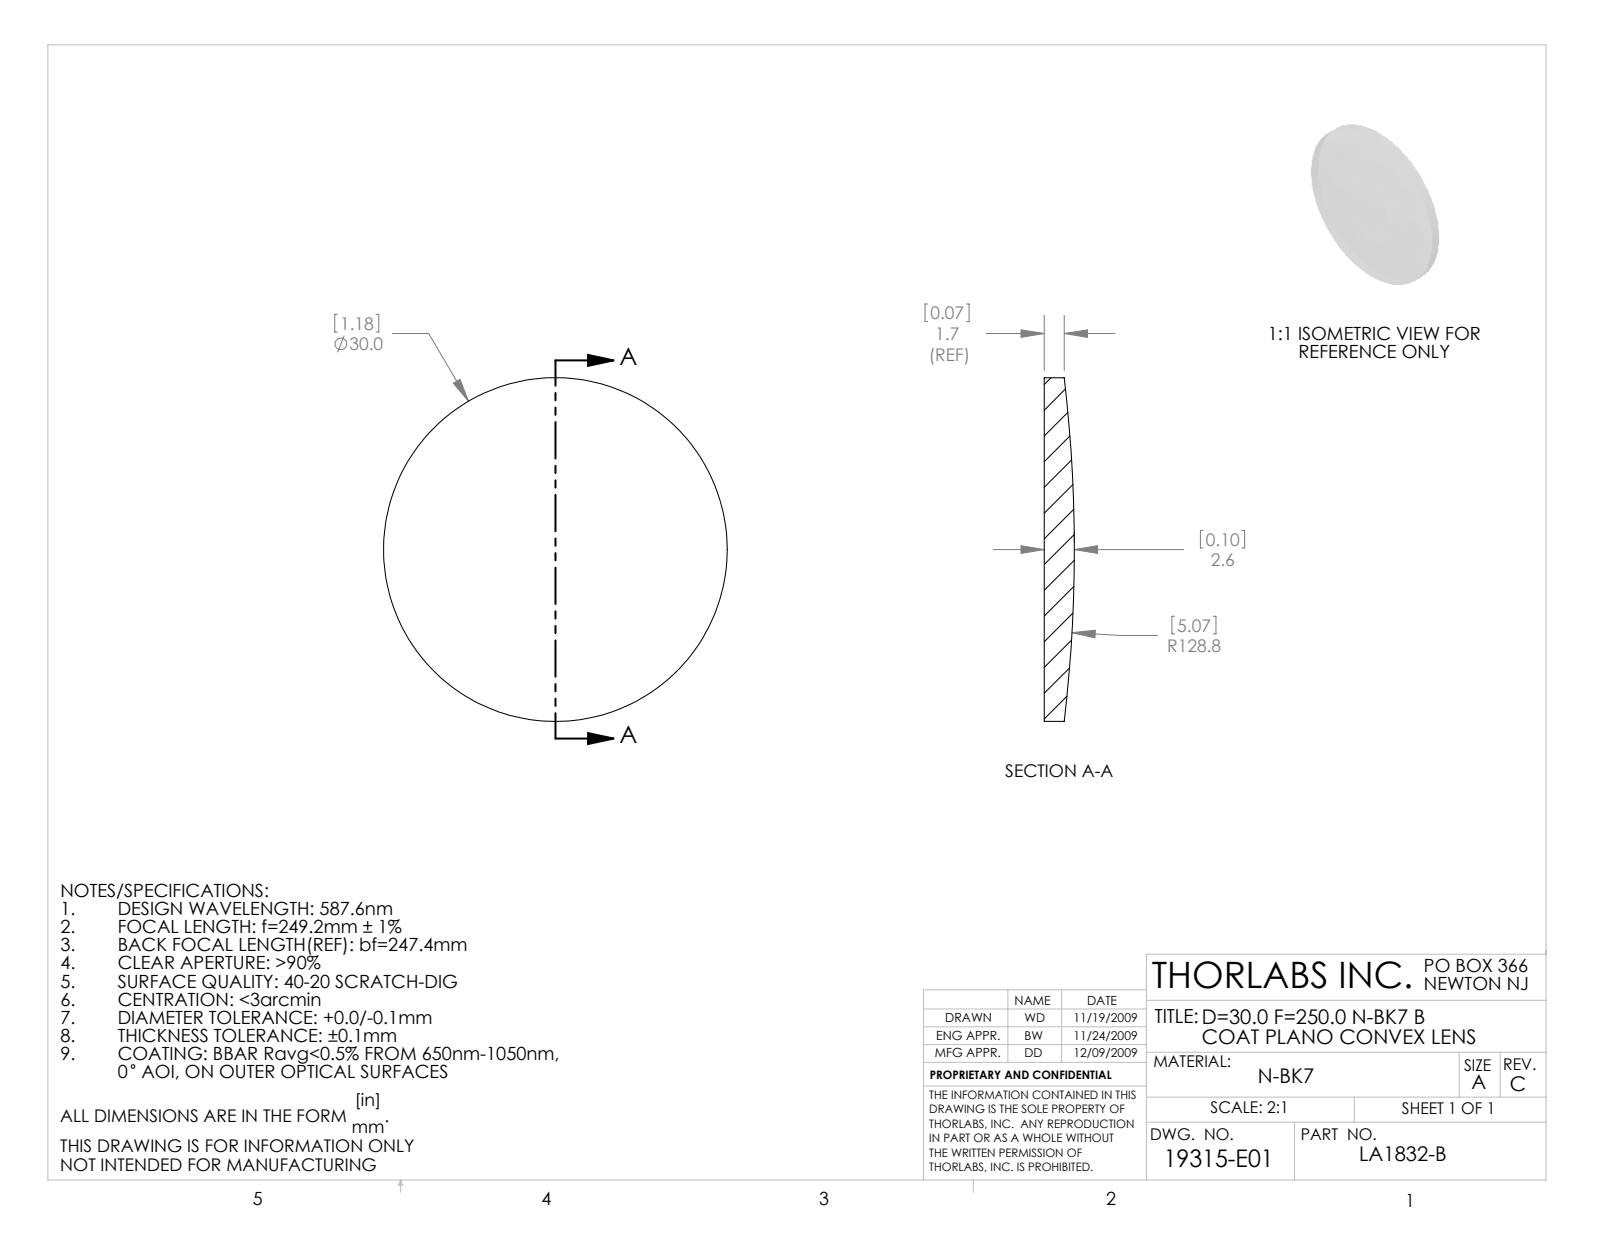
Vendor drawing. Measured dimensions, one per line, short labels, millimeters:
name: 19315-E0W
written by: SolidWorks 2009 (AUTOMOTIVE_DESIGN)
unit: mm
bodies: 1 solid, 5 faces (1 planar, 2 cylindrical, 2 other)
size: 30 × 30 × 2.62
volume: 1 542 mm³; area: 1 580 mm²
bosses: 1× ⌀30
